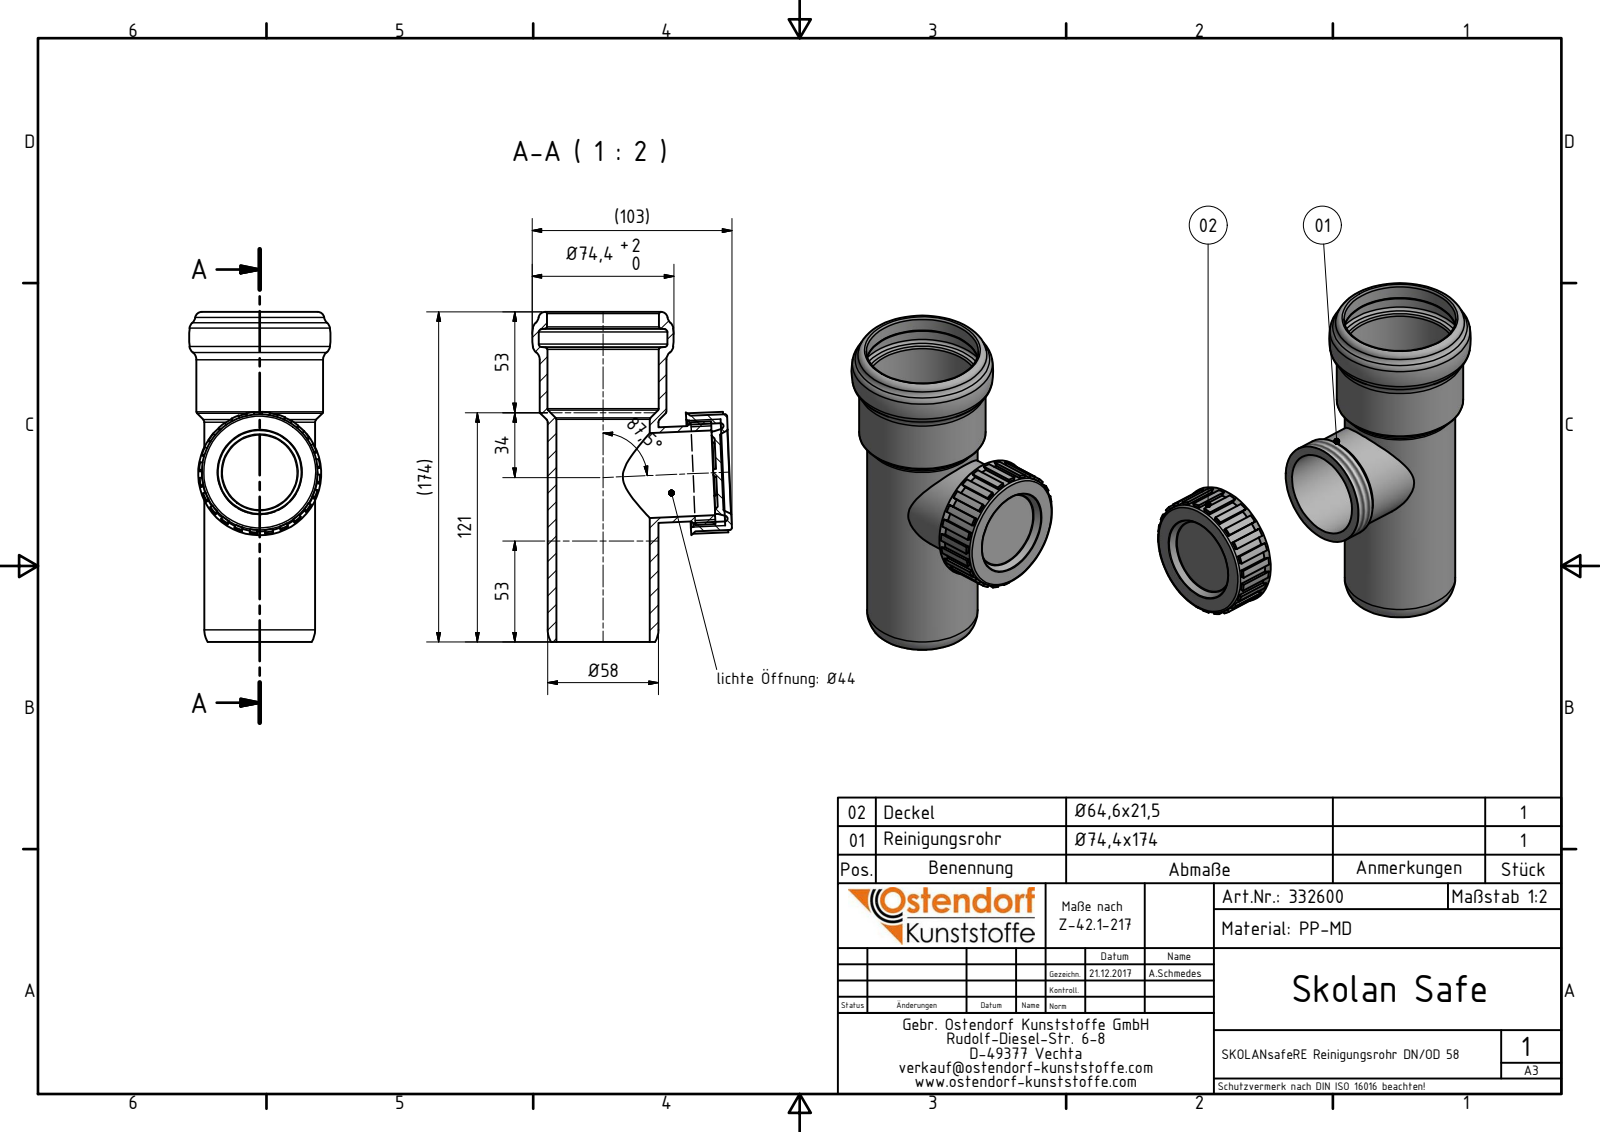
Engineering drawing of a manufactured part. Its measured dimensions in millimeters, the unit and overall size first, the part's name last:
Units: millimetres
Overall size (bounding box): 173.3 × 104.87 × 74.4
Round holes (diameter × count): ⌀44.5 ×1, ⌀49.1 ×1, ⌀51.6 ×1, ⌀56 ×1, ⌀58.5 ×1, ⌀58.8 ×1, ⌀67.6 ×1
Round bosses / shafts (diameter × count): ⌀66.5 ×1, ⌀60.8 ×1, ⌀58.1 ×1, ⌀54 ×1, ⌀50.2 ×1, ⌀43.4 ×1
Partial cylindrical surfaces — rounded edges, fillets, slot ends (radius × count): R0.5 ×4, R31.75 ×1
Main face-to-face distances: 3.99, 2.99, 6.98, 1.52, 4.51, 8.5, 13, 14.52, 17.51, 21.5
Volume: 175 054 mm³ · Surface area: 89 377 mm²
Bodies: 2 solids, 174 faces (91 planar, 45 cylindrical, 38 other)
Part name (STEP PRODUCT): 332600 SKRE Reinigungsrohr DN_OD 58; 332600 SKRE Reinigungsrohr DN_OD 58 Deckel; 332600 SKOLANsafeRE Reinigungsrohr DN_OD 58
STEP written by: Autodesk Inventor 2016 (AUTOMOTIVE_DESIGN)
